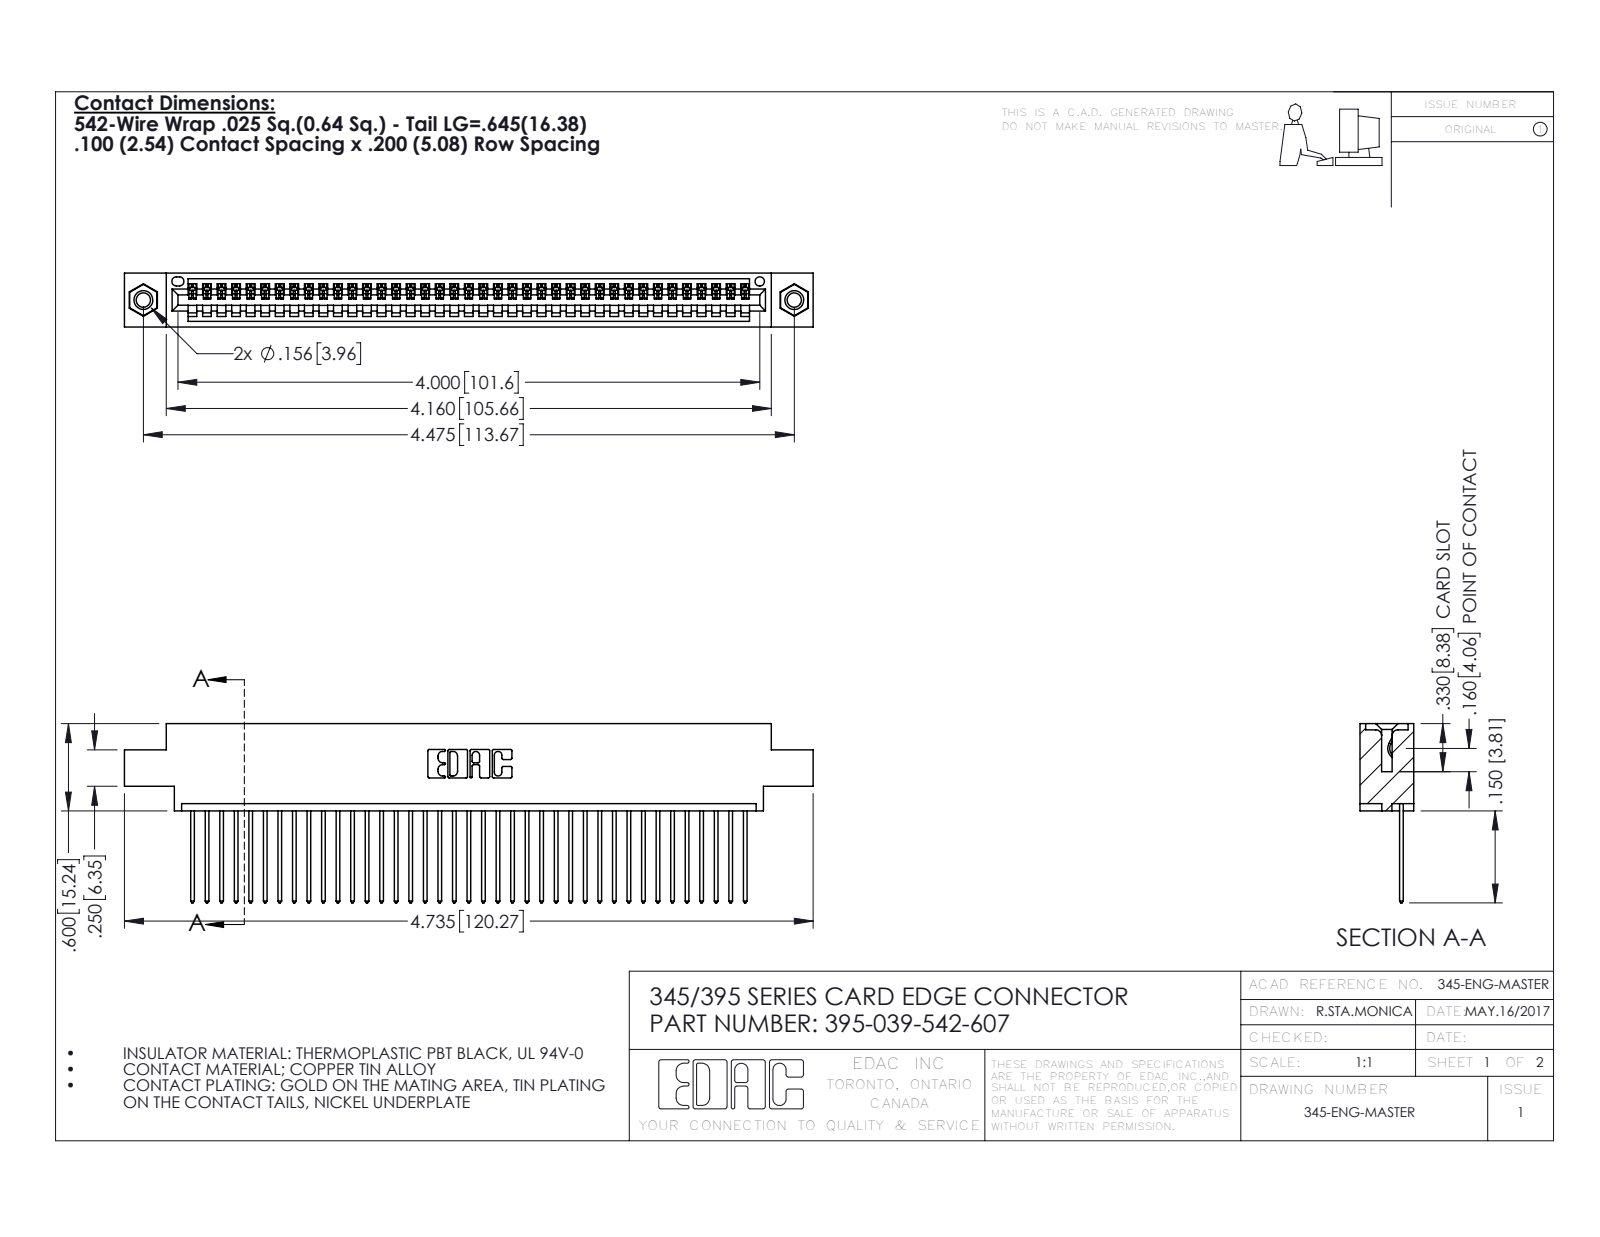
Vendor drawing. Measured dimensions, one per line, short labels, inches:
name: 345-250-001_345-250-005-103; 395-039-542-607; 345-292-001_345-293-142; 345 Part_0.170 Offset - 0.156 Dia-TI
written by: SolidWorks 2016 (CONFIG_CONTROL_DESIGN)
unit: in
bodies: 42 solids, 2452 faces (1676 planar, 760 cylindrical, 16 other)
size: 4.735 × 1.232 × 0.37
volume: 0.693 in³; area: 24.43 in²
holes: 2× ⌀0.098, 2× ⌀0.125, 2× ⌀0.156, 1× ⌀0.064
bosses: 2× ⌀0.155
rounds: 78× R0.006, 78× R0.01, 22× R0.01, 6× R0.007, 6× R0.031, 3× R0.026, 2× R0.031, 2× R0.04
face distances: 0.072, 0.298, 0.37, 0.098, 0.272, 0.025, 0.2, 0.225, 0.175, 0.149
hole spacings: 0.27, 4.239, 4.475
